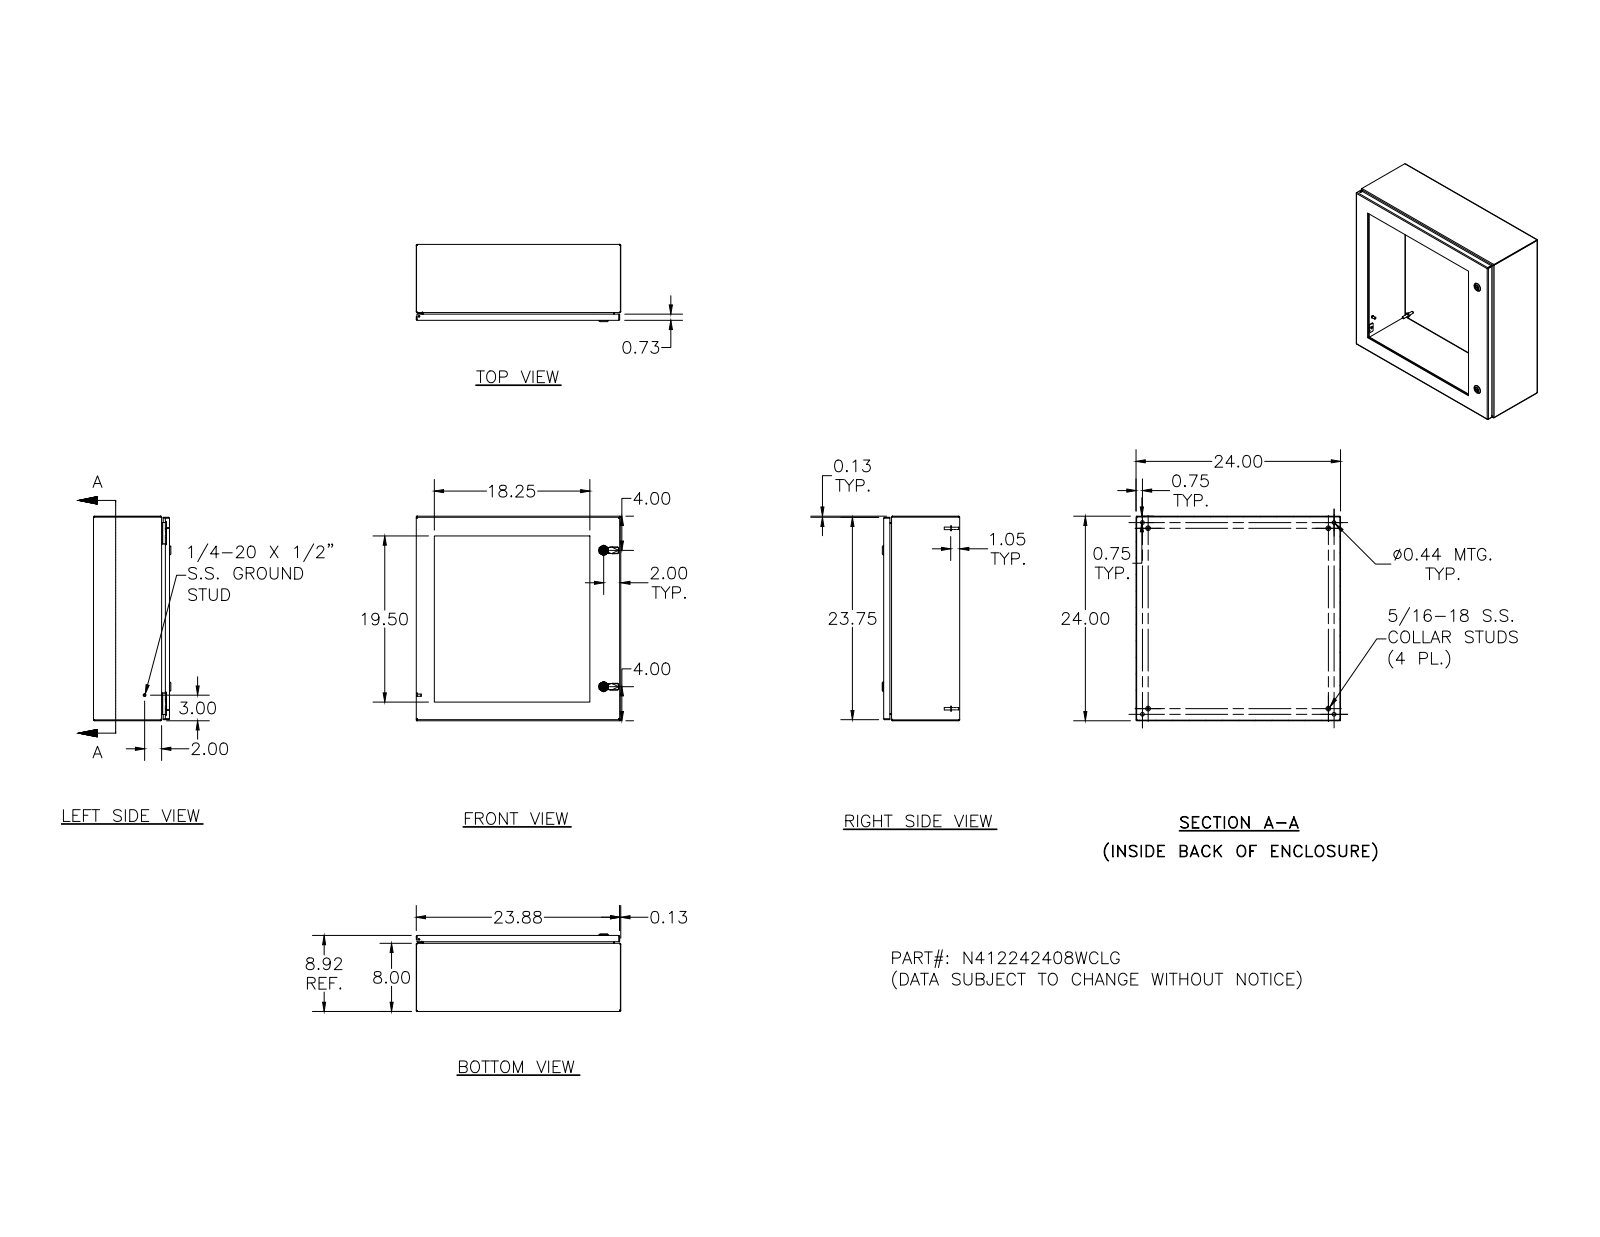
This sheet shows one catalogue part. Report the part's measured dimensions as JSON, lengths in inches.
{"part_name": "N412242408WCLG", "step_written_by": "SolidWorks 2018 (AUTOMOTIVE_DESIGN)", "units": "inches", "bodies": {"solids": 84, "faces": 2510, "planar": 971, "cylindrical": 762, "other": 777}, "overall_size": [24, 24, 9.075], "volume_in3": 236, "surface_area_in2": 4559, "round_holes": [[0.156, 22], [0.281, 20], [0.188, 5], [0.093, 4], [0.152, 4], [0.167, 4], [0.172, 4], [0.437, 4], [0.197, 2], [0.315, 2], [0.394, 2], [0.402, 2]], "round_bosses_or_shafts": [[0.337, 20], [0.19, 20], [0.25, 10], [0.563, 4], [0.36, 4], [0.32, 4], [0.3, 4], [0.275, 4]], "partial_cylinders_radius": [[0.012, 54], [0.031, 34], [0.05, 26], [0.105, 24], [0.02, 23], [0.016, 18], [0.125, 16], [0.032, 8]], "face_to_face_distances": [0.074, 8.843, 23.926, 8.769, 0.25, 8.593, 8.519, 24, 23.852, 8.917], "hole_center_spacings": [4, 8, 21.132, 12, 20, 22.239, 20.75, 6.221]}
